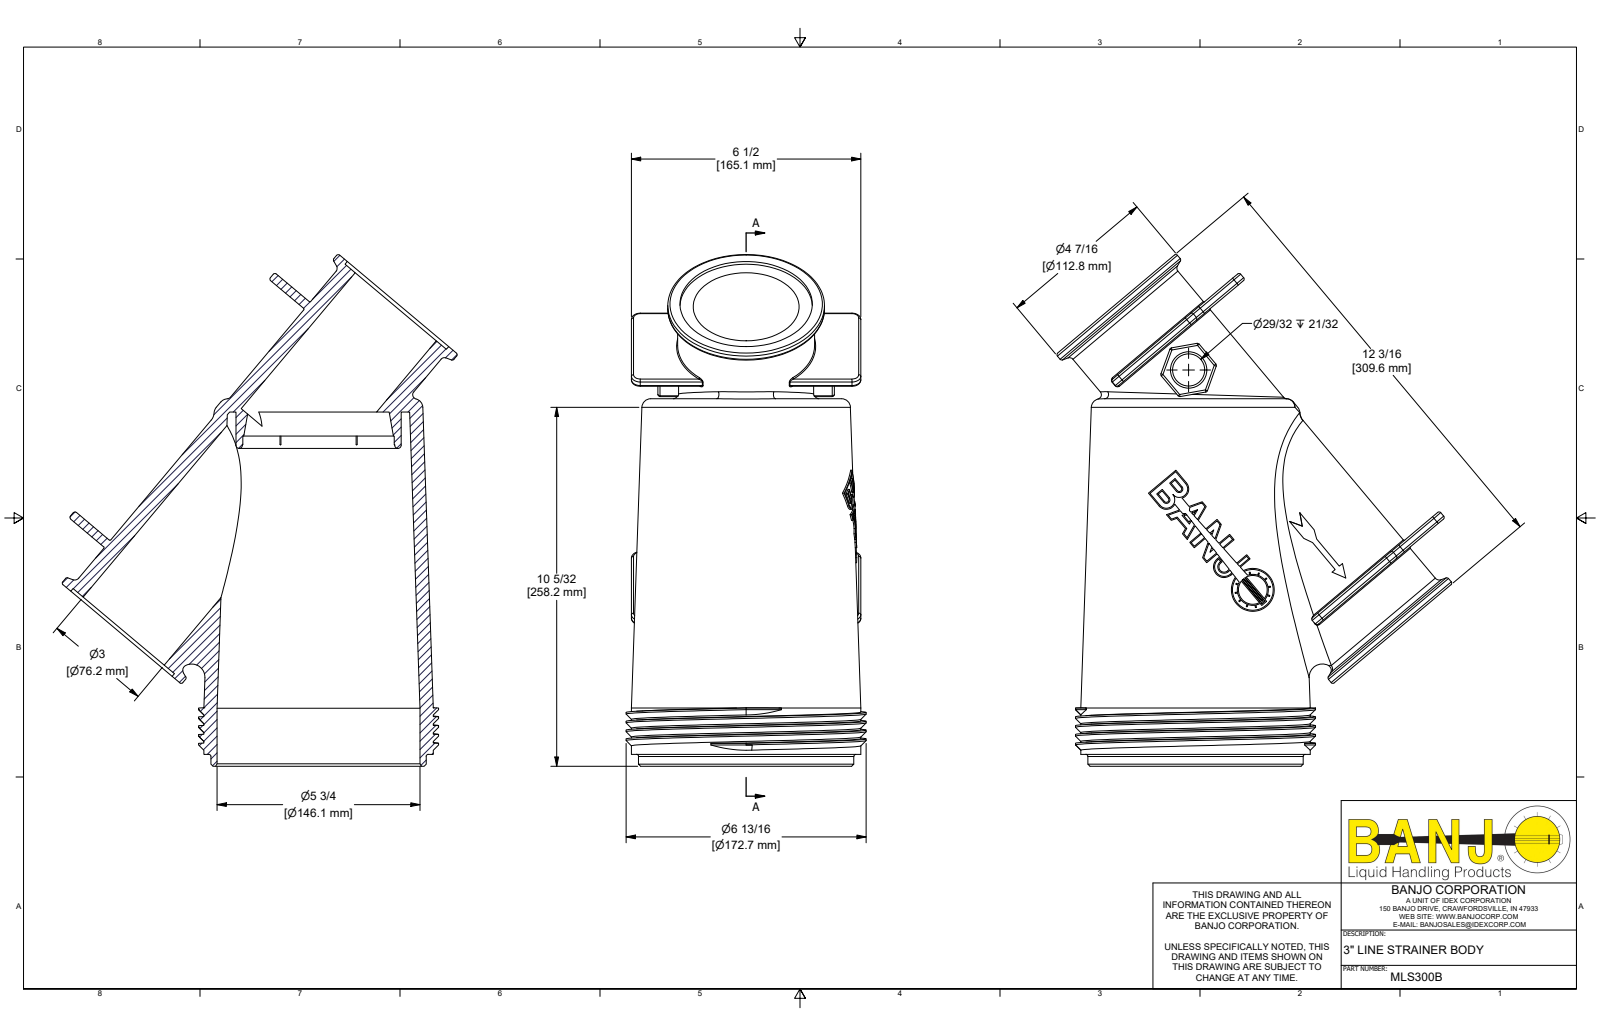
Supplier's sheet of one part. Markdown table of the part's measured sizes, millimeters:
| quantity | value |
| --- | --- |
| part name | MLS300B |
| STEP written by | Autodesk Inventor 2022 (AUTOMOTIVE_DESIGN) |
| units | millimeters |
| bodies | 1 solid, 532 faces (235 planar, 158 cylindrical, 139 other) |
| overall size | 368 × 284.1 × 172.7 |
| volume | 2 007 000 mm³ |
| surface area | 441 600 mm² |
| round holes (diameter × count) | 95.3 × 2, 20.8 × 1, 23.1 × 1, 29.3 × 1, 76.2 × 1, 109.7 × 1, 146.1 × 1 |
| round bosses / shafts (diameter × count) | 112.8 × 2, 98.6 × 2, 172.7 × 1, 165.1 × 1, 154.9 × 1, 118.9 × 1, 30.9 × 1 |
| partial cylindrical surfaces (radius × count) | 1.5 × 46, 6.4 × 17, 0.4 × 6, 0.8 × 4, 1.8 × 2, 2.6 × 2, 6 × 2, 6.8 × 2 |
| main face-to-face distances | 6.4, 223.9, 217.5, 230.3, 223.9, 6.4, 43.5, 261, 39.7, 269.9 |
| hole center spacings | 164.8 |
